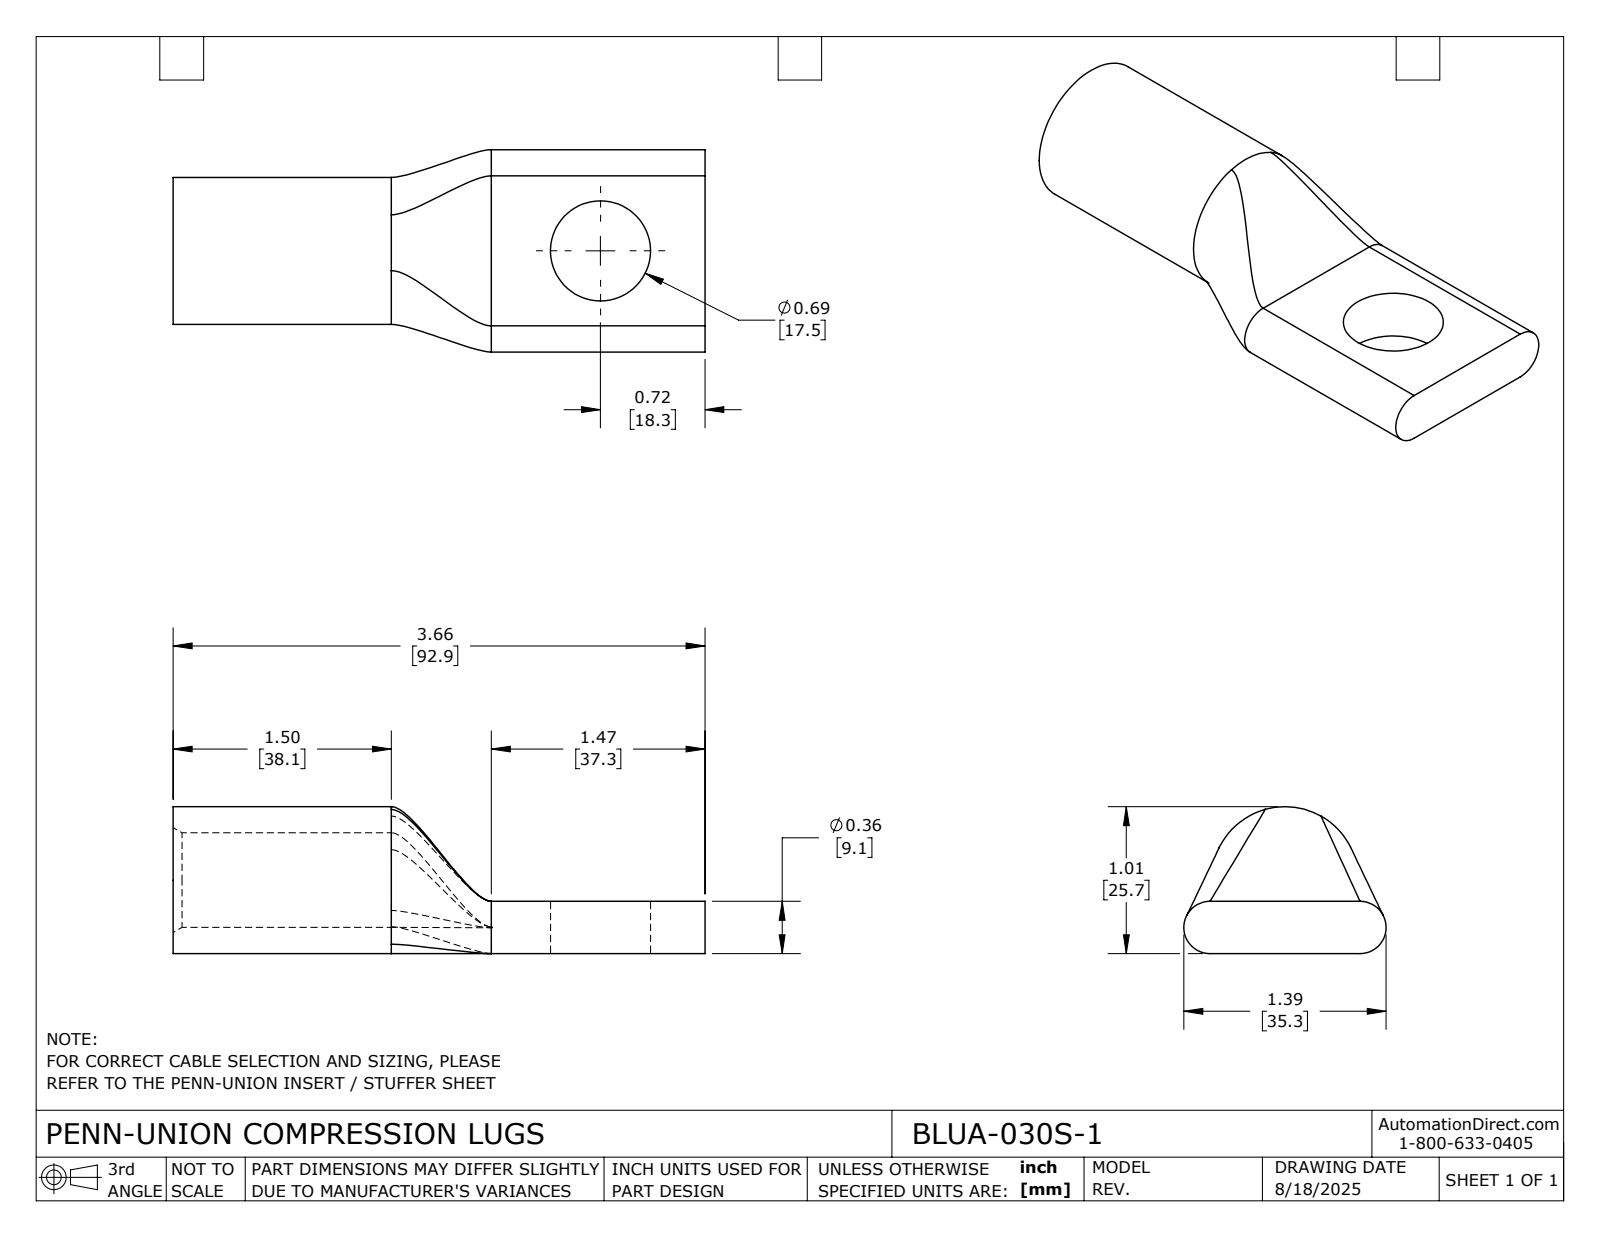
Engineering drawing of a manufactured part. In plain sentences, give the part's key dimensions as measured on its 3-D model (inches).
The part is named "BLUA-030S-1". Its 3-D file was written by "SolidWorks 2024 (CONFIG_CONTROL_DESIGN)". It is 1 solid with 24 faces: 5 planar, 9 cylindrical and 10 other. Overall it measures 3.656 by 1.391 by 1.01 inches. Its volume is 1.583 cubic inches and its surface area 17.46 square inches. Round holes: 1 of diameter 0.65, 1 of diameter 0.687. Round bosses or shafts: 1 of diameter 1.01. Partial cylindrical surfaces (rounded edges, fillets, slot ends): 2 of radius 0.18. The main face-to-face distances are 0.359, 3.656, 2.187, 1.469.
